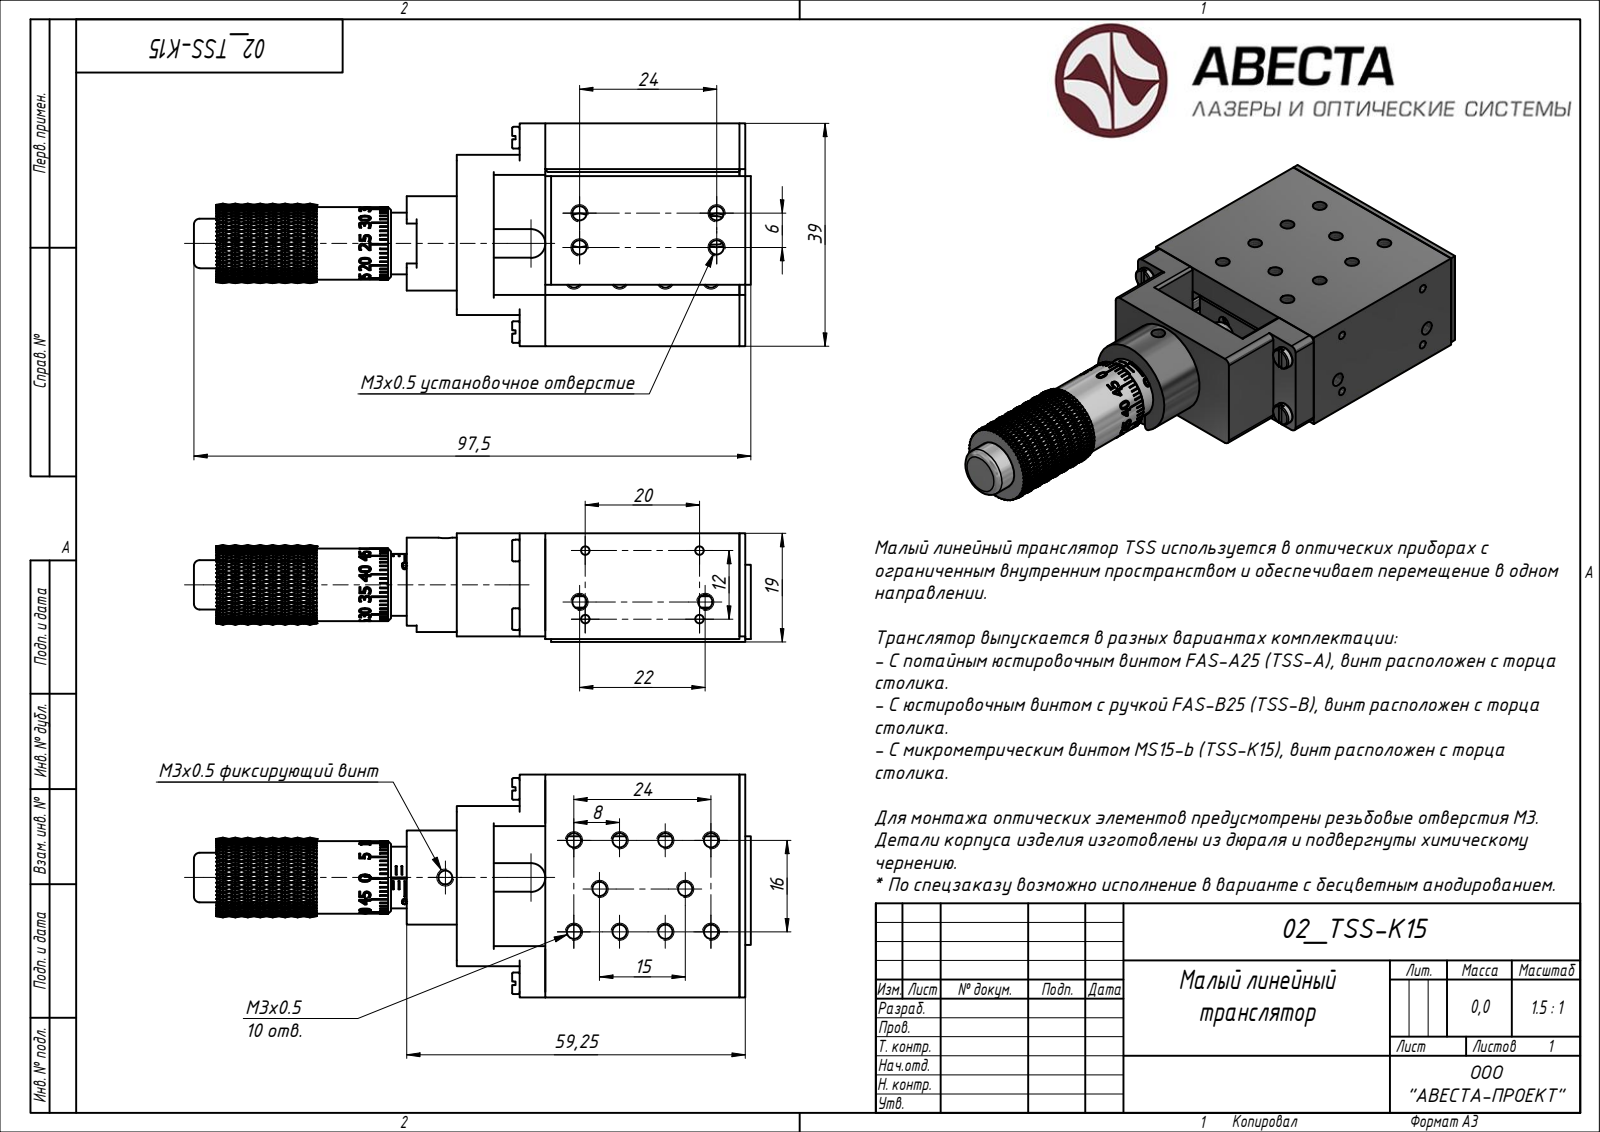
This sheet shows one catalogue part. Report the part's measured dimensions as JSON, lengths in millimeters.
{"step_written_by": "Rhino 7.34 (AUTOMOTIVE_DESIGN)", "units": "millimeters", "bodies": {"solids": 3, "faces": 3562, "planar": 2887, "cylindrical": 345, "other": 330}, "overall_size": [97.5, 39, 19], "volume_mm3": 31609, "surface_area_mm2": 23304, "round_holes": [[2.46, 19], [1.57, 6], [2.5, 6], [1.5, 4], [2.4, 4], [1.57, 2], [2.46, 2], [5.5, 1], [6, 1], [9.5, 1], [11, 1]], "round_bosses_or_shafts": [[4, 8], [3.8, 4], [2, 4], [16.5, 1], [13.5, 1], [12.7, 1], [10.8, 1], [8.66, 1]], "partial_cylinders_radius": [[0.5, 8], [1, 8], [2, 4], [0.78, 2], [0.78, 1], [1.8, 1], [5.39, 1], [6.25, 1]], "face_to_face_distances": [1, 0.5, 4.5, 13.5, 5.5, 12, 2, 11.5, 1.5, 13], "hole_center_spacings": [16, 6, 8, 17.89, 3.16, 7, 12, 20.88]}
